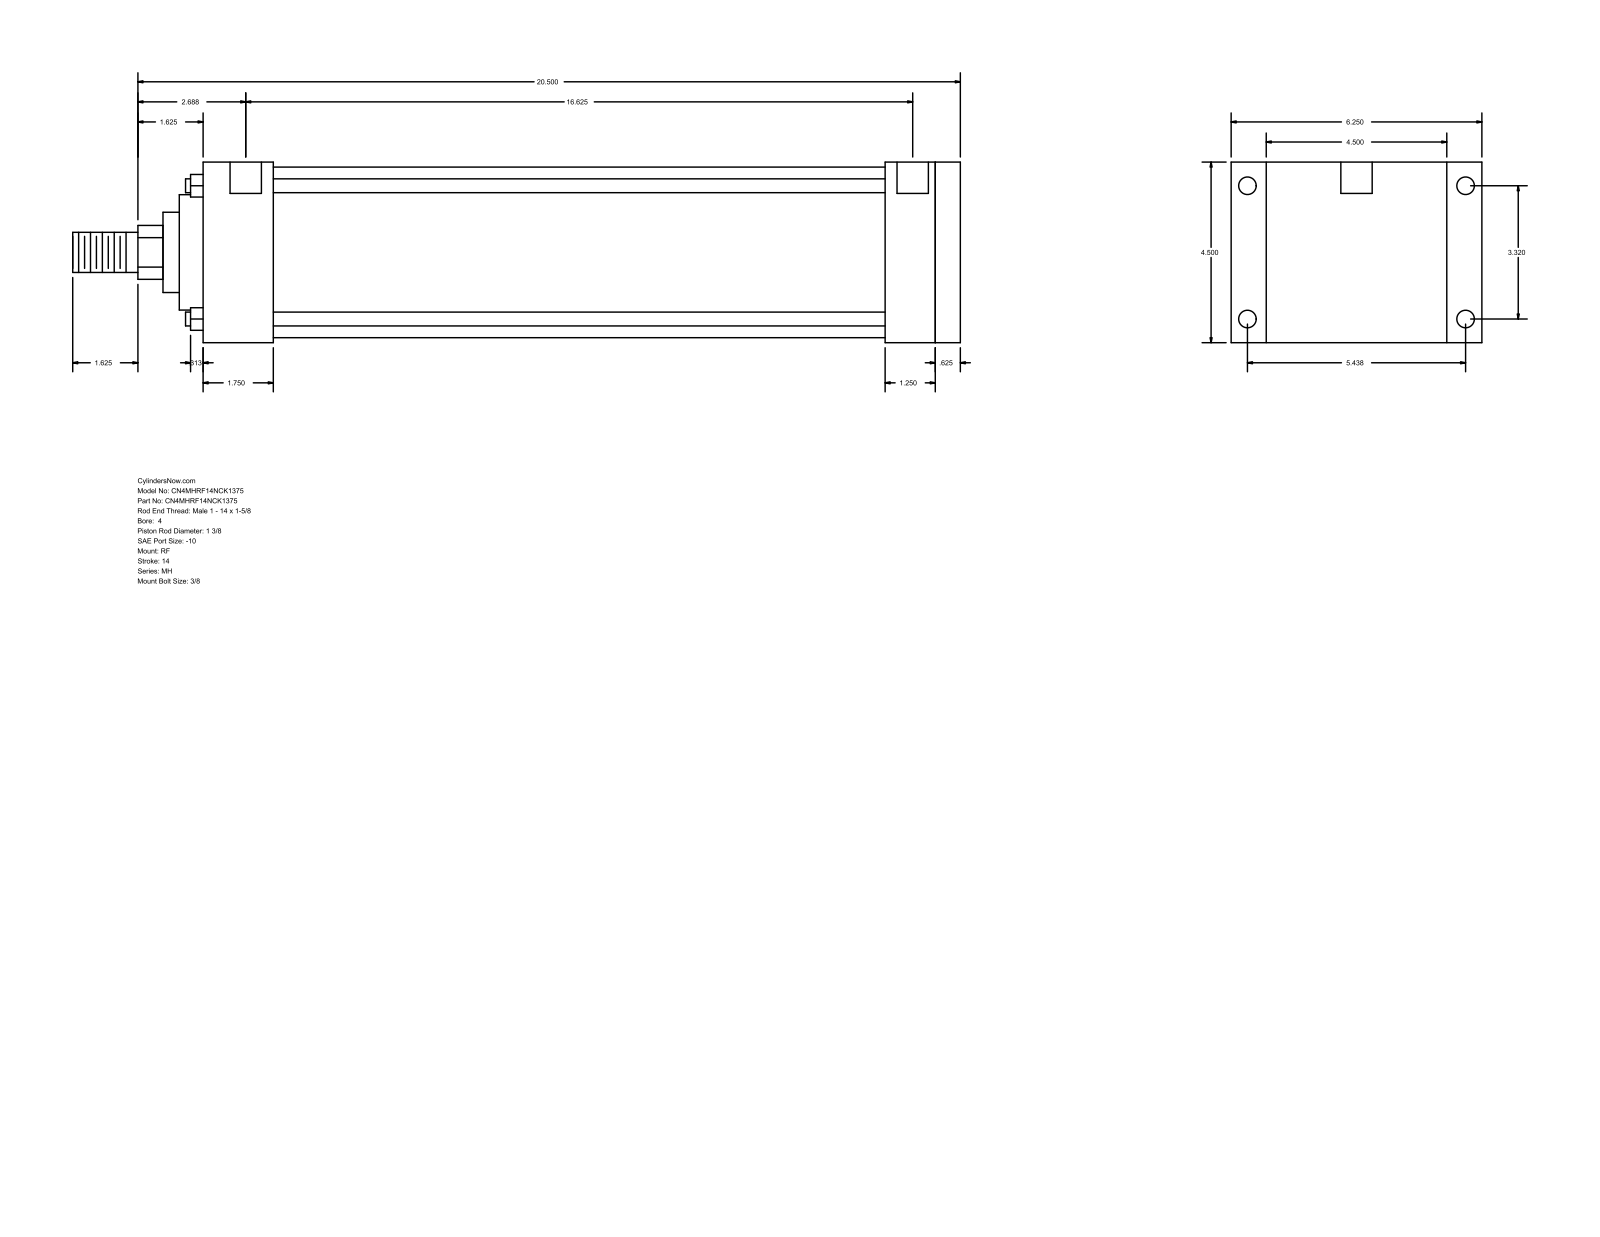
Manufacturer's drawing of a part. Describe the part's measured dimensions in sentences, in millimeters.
The part is named "MH_RF__0400_1.375". Its 3-D file was written by "GSSL Pune (CONFIG_CONTROL_DESIGN)". It is 0 solids with 94 faces: 65 planar, 29 cylindrical and 0 other. Overall it measures 561.98 by 158.75 by 114.3 millimeters. Round holes: 4 of diameter 8.73, 4 of diameter 11.13, 2 of diameter 19.84. Round bosses or shafts: 4 of diameter 8.76, 1 of diameter 107.95, 1 of diameter 73.03, 1 of diameter 50.8, 1 of diameter 34.92, 1 of diameter 25.4. Partial cylindrical surfaces (rounded edges, fillets, slot ends): 1 of radius 17.06. The main face-to-face distances are 114.3, 479.43, 15.88, 463.55, 44.45, 419.1, 434.98, 431.8, 387.35, 31.75. The hole center spacings are 84.32, 138.12, 161.82, 425.45, 1.58, 1.59, 422.28, 423.86.
